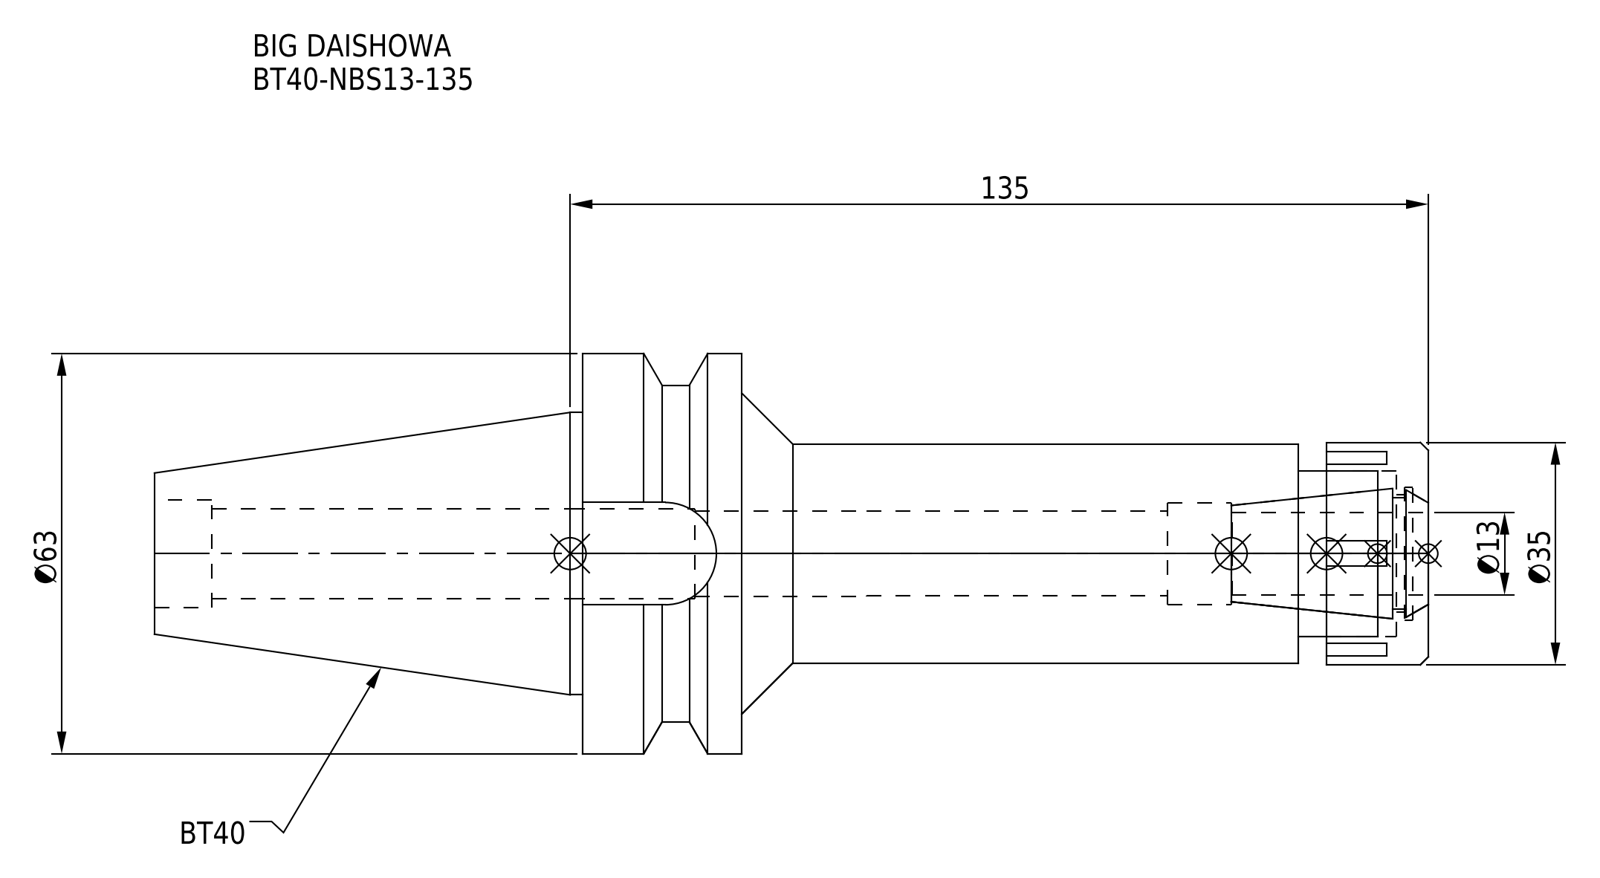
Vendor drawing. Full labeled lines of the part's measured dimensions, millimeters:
Part name (STEP PRODUCT): BT40-NBS13-135.stp; BT40-NBS13-135; DXF_TEMP_ASSY_ASM_4_ASM.stp; BT40-NBS13-135_1.stp (+3 more)
STEP written by: SolidWorks 2019 (CONFIG_CONTROL_DESIGN)
Units: millimetres
Bodies: 2 solids, 93 faces (45 planar, 34 cylindrical, 14 other)
Overall size (bounding box): 200.4 × 63 × 63
Volume: 202 116 mm³ · Surface area: 41 966 mm²
Round holes (diameter × count): ⌀13.3 ×1, ⌀13.5 ×1, ⌀14.2 ×1, ⌀16 ×1, ⌀17 ×1, ⌀18.5 ×1, ⌀21 ×1, ⌀26 ×1
Round bosses / shafts (diameter × count): ⌀63 ×1, ⌀53 ×1, ⌀44.45 ×1, ⌀35 ×1, ⌀34.5 ×1
Partial cylindrical surfaces — rounded edges, fillets, slot ends (radius × count): R8.05 ×1
Main face-to-face distances: 25, 108, 133, 20.5, 92, 8, 87.5, 112.5, 16, 4.5
